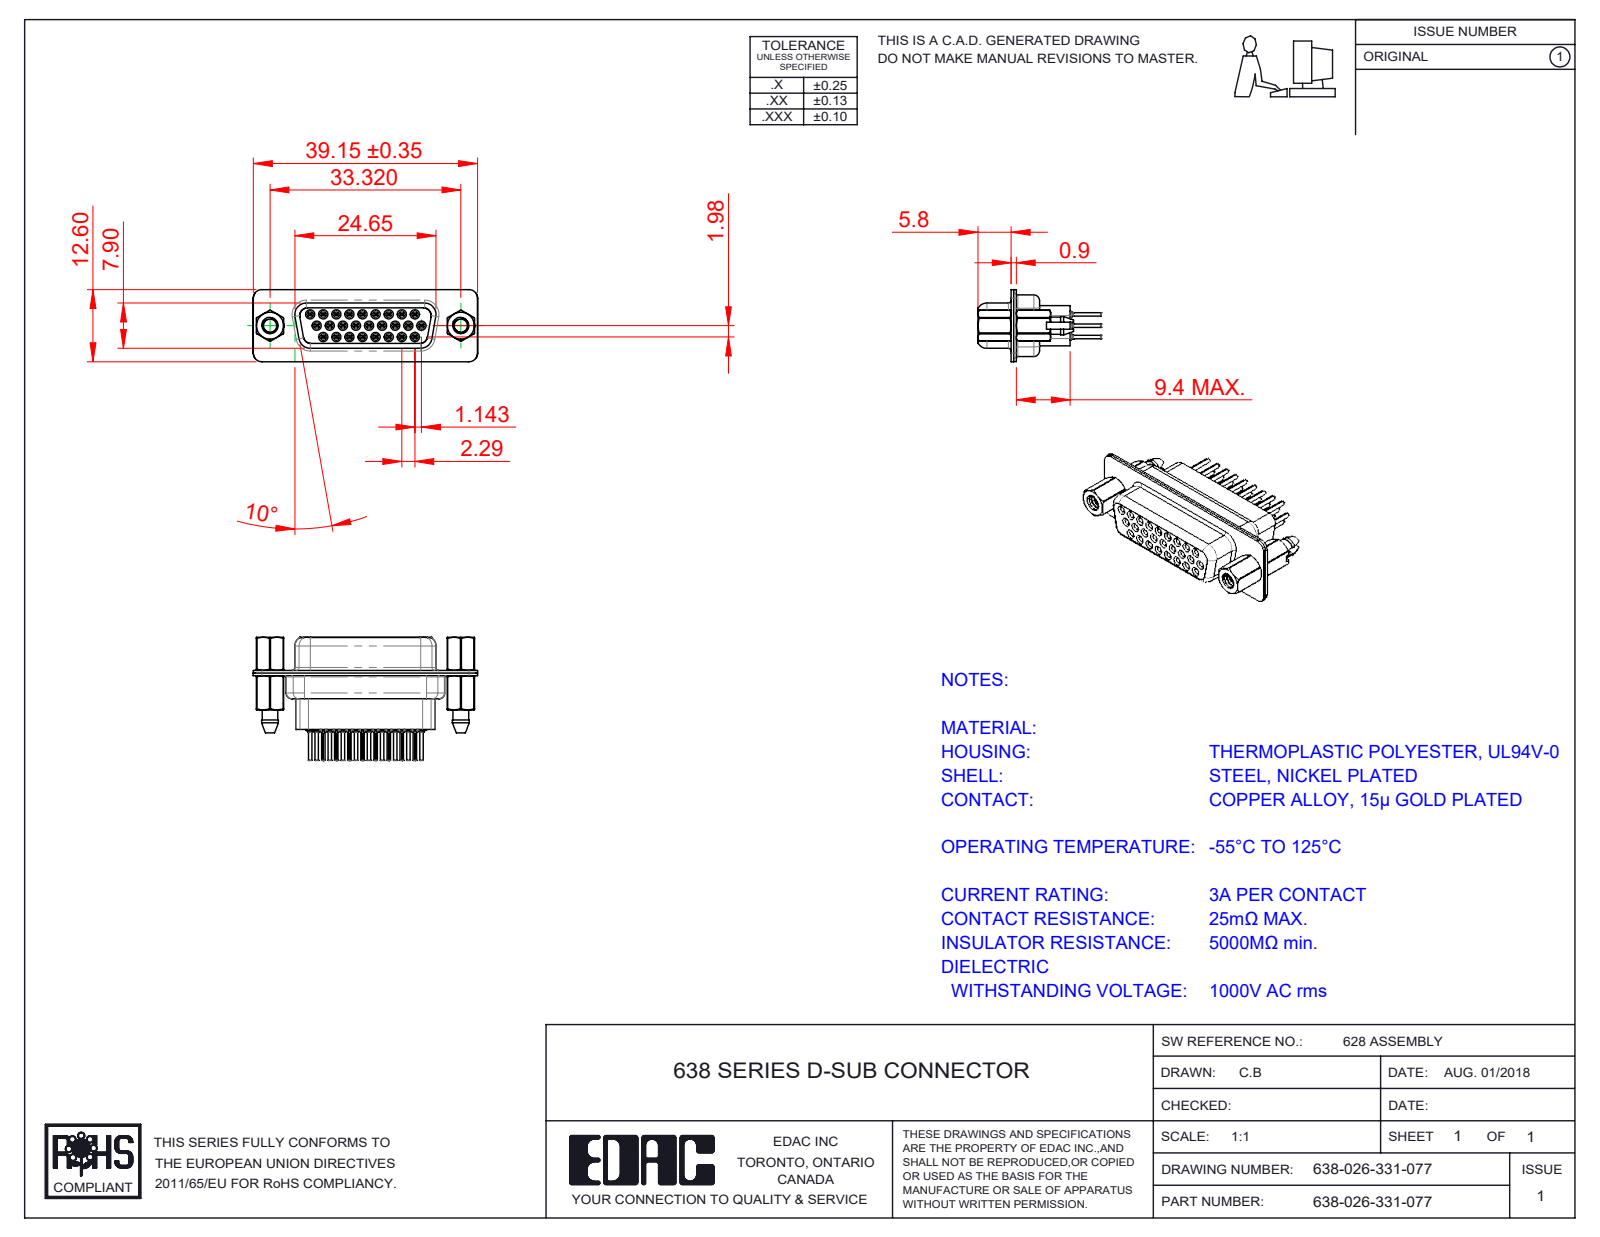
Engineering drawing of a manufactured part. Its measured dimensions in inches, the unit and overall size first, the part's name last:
Units: inches
Overall size (bounding box): 1.543 × 0.846 × 0.496
Round holes (diameter × count): ⌀0.008 ×26, ⌀0.031 ×26, ⌀0.039 ×26, ⌀0.043 ×26, ⌀0.063 ×26, ⌀0.067 ×26, ⌀0.071 ×26, ⌀0.089 ×2, ⌀0.09 ×2, ⌀0.157 ×2, ⌀0.159 ×2, ⌀0.191 ×2
Round bosses / shafts (diameter × count): ⌀0.079 ×26, ⌀0.059 ×26, ⌀0.047 ×26, ⌀0.024 ×26, ⌀0.195 ×2, ⌀0.189 ×2, ⌀0.11 ×2
Partial cylindrical surfaces — rounded edges, fillets, slot ends (radius × count): R0.004 ×52, R0.059 ×22, R0.011 ×18, R0.079 ×12, R0.061 ×8, R0.053 ×5, R0.01 ×4, R0.02 ×4
Main face-to-face distances: 0.018, 0.016, 0.26, 0.056, 0.35, 0.035, 0.276, 0.187, 0.09, 0.228
Hole centre spacings: 0.156, 0.09, 0.18, 0.238, 0.09, 0.324, 0.27, 0.413
Volume: 0.183 in³ · Surface area: 16.49 in²
Bodies: 33 solids, 3677 faces (927 planar, 1099 cylindrical, 1651 other)
Part name (STEP PRODUCT): 638 4-40 Threaded Boardlock_LP; 638-026-331-077; 638 Contact Row 1_31; 638 Housing_26 Contacts HP (+5 more)
STEP written by: SolidWorks 2020 (CONFIG_CONTROL_DESIGN)
